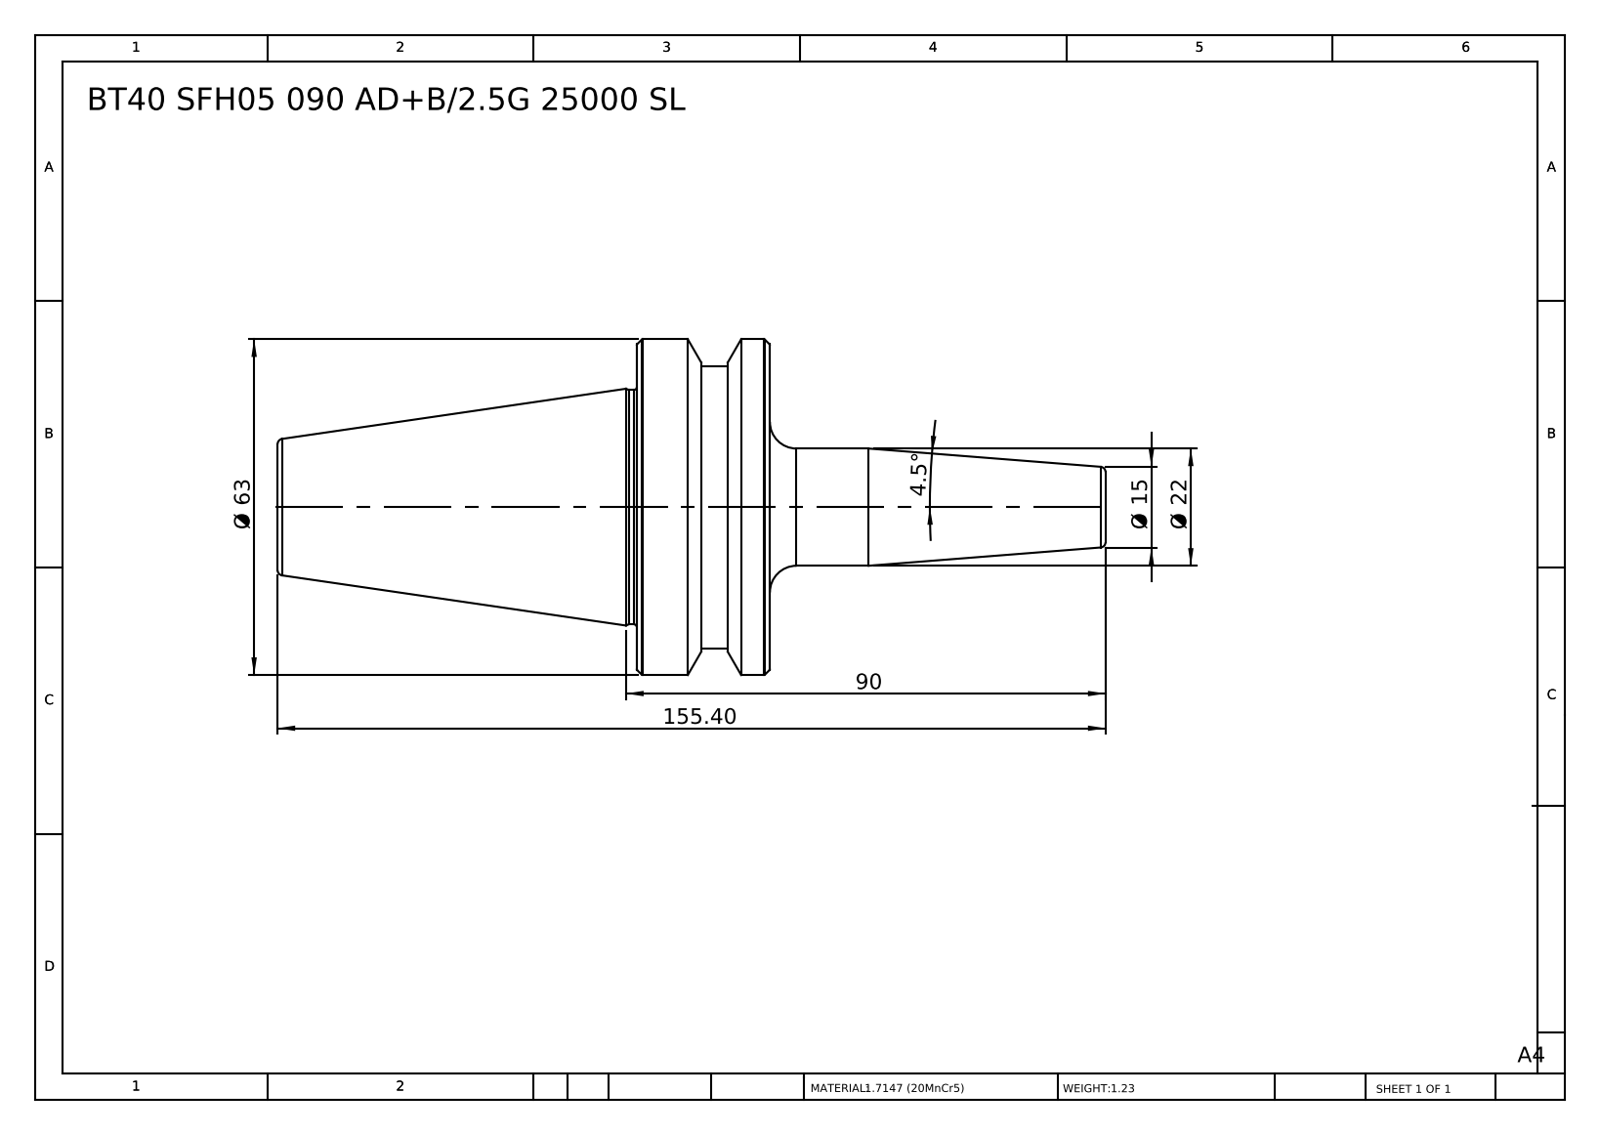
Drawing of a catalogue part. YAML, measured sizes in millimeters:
part_name: "BT40 SFH05 090 AD+B-2.5G 25000 SL"
step_written_by: "SolidWorks 2014 (CONFIG_CONTROL_DESIGN)"
units: millimeters
bodies: {solids: 1, faces: 46, planar: 6, cylindrical: 10, other: 30}
overall_size: [155.4, 63, 63]
volume: 157882
surface_area: 21836
round_bosses_or_shafts:
  - {diameter: 63, count: 1}
  - {diameter: 53, count: 1}
  - {diameter: 44, count: 1}
  - {diameter: 22, count: 1}
face_to_face_distances: [25, 92.4, 67.4, 63, 88, 155.4, 70.9, 7.9, 17.1, 84.5]
